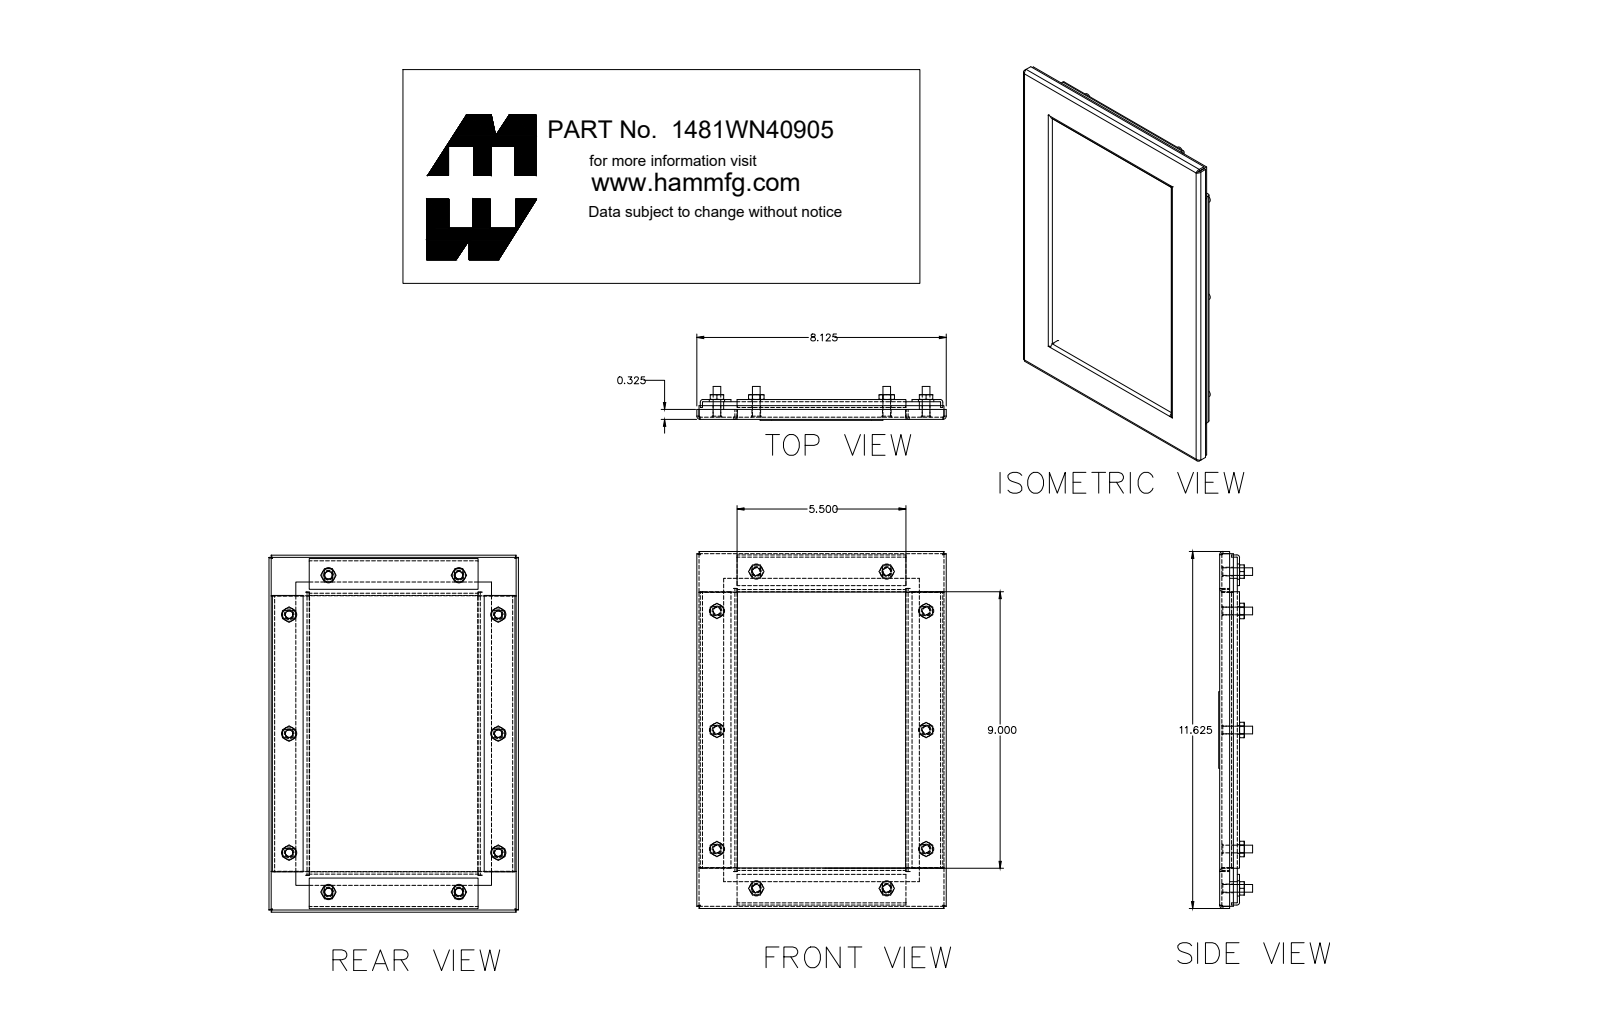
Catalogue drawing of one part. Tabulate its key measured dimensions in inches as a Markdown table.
| quantity | value |
| --- | --- |
| part name | 1481WN40905_Default |
| STEP written by | SolidWorks 2019 (CONFIG_CONTROL_DESIGN) |
| units | inches |
| bodies | 27 solids, 466 faces (224 planar, 104 cylindrical, 138 other) |
| overall size | 12.025 × 8.525 × 1.072 |
| volume | 27.32 in³ |
| surface area | 468.1 in² |
| round holes (diameter × count) | 0.25 × 10, 0.328 × 10 |
| round bosses / shafts (diameter × count) | 0.313 × 10, 0.25 × 10 |
| partial cylindrical surfaces (radius × count) | 0.036 × 8, 0.108 × 8, 0.016 × 4, 0.088 × 4 |
| main face-to-face distances | 0.072, 0.575, 0.503, 0.325, 0.253, 0.25, 0.575, 0.647, 0.322, 0.072 |
| hole center spacings | 6.813, 10.313, 1.812, 5.313, 7.837, 9.122, 3.875, 7.838 |
